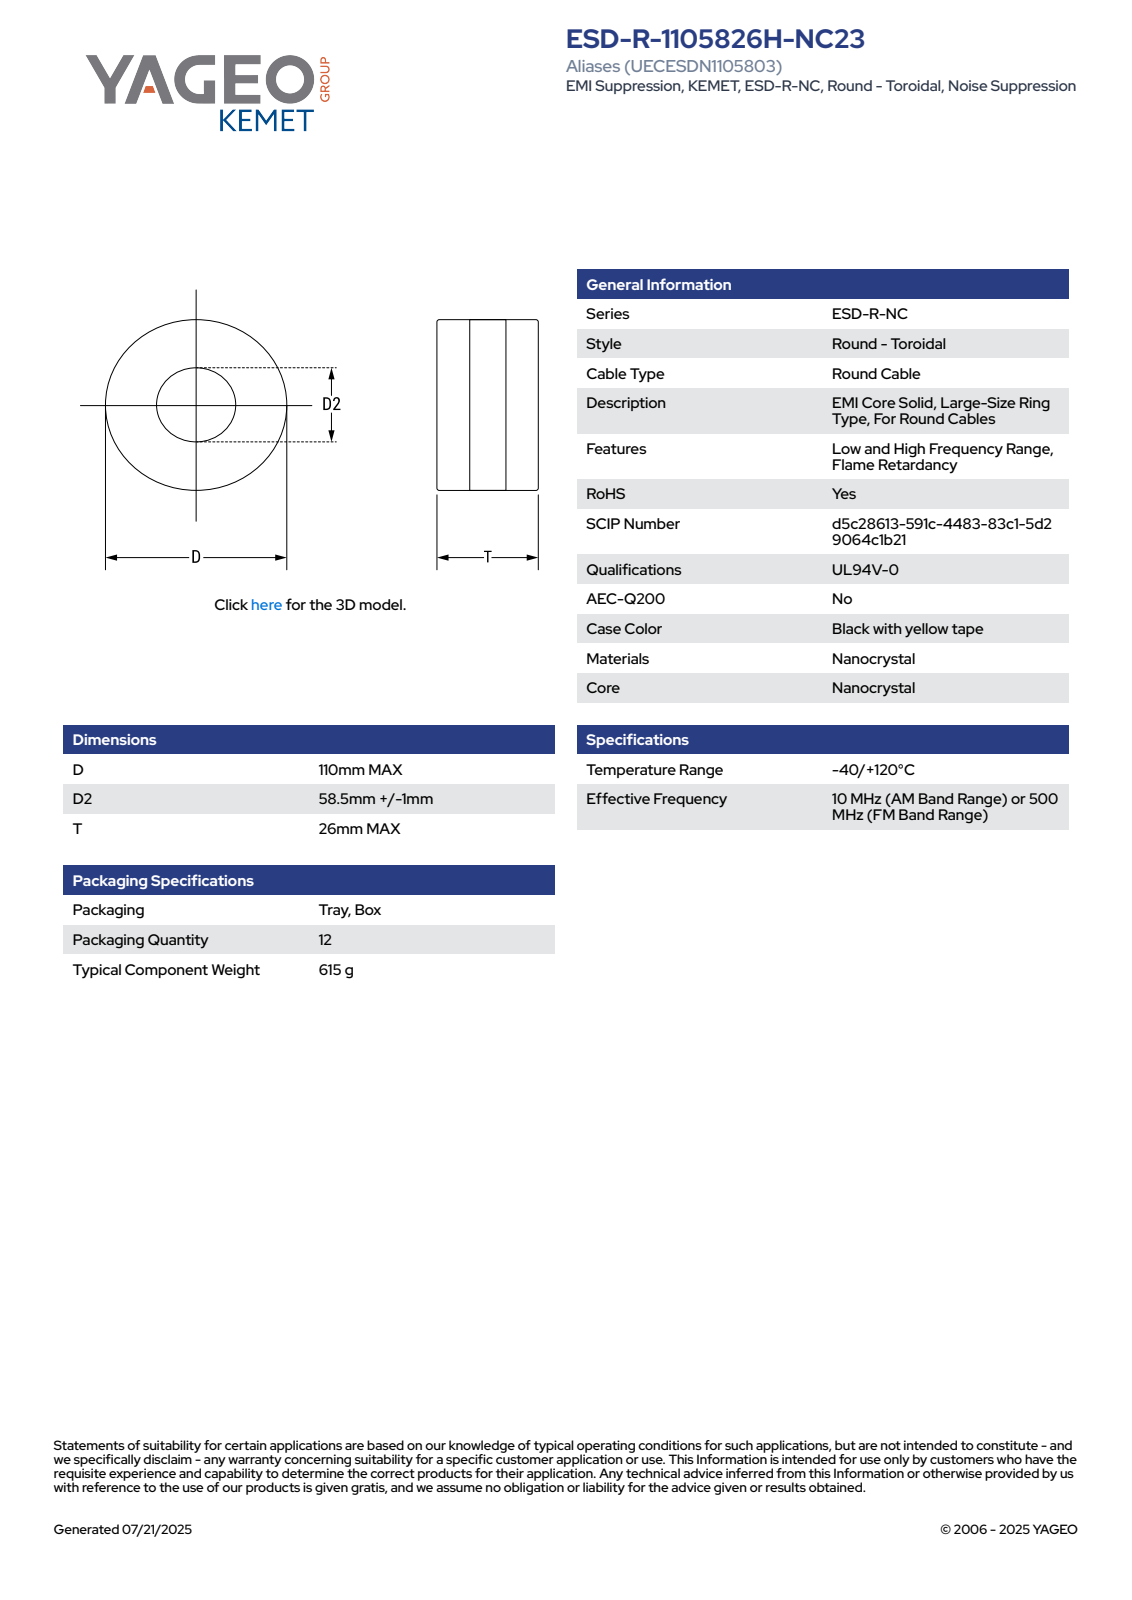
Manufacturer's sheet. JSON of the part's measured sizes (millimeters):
{"part_name": "EC_ESDRNC23_D110D259.5T26", "step_written_by": "SolidWorks 2014 (AUTOMOTIVE_DESIGN)", "units": "millimeters", "bodies": {"solids": 1, "faces": 74, "planar": 26, "cylindrical": 9, "other": 39}, "overall_size": [110.03, 110.02, 26], "volume_mm3": 174721, "surface_area_mm2": 26969, "round_holes": [[59.5, 1]], "round_bosses_or_shafts": [[110.02, 1], [110, 1]], "partial_cylinders_radius": [[55.02, 1]], "face_to_face_distances": [26, 9, 25.25, 16.25, 17, 0.75, 11.54, 2.54, 13.71, 14.46]}
